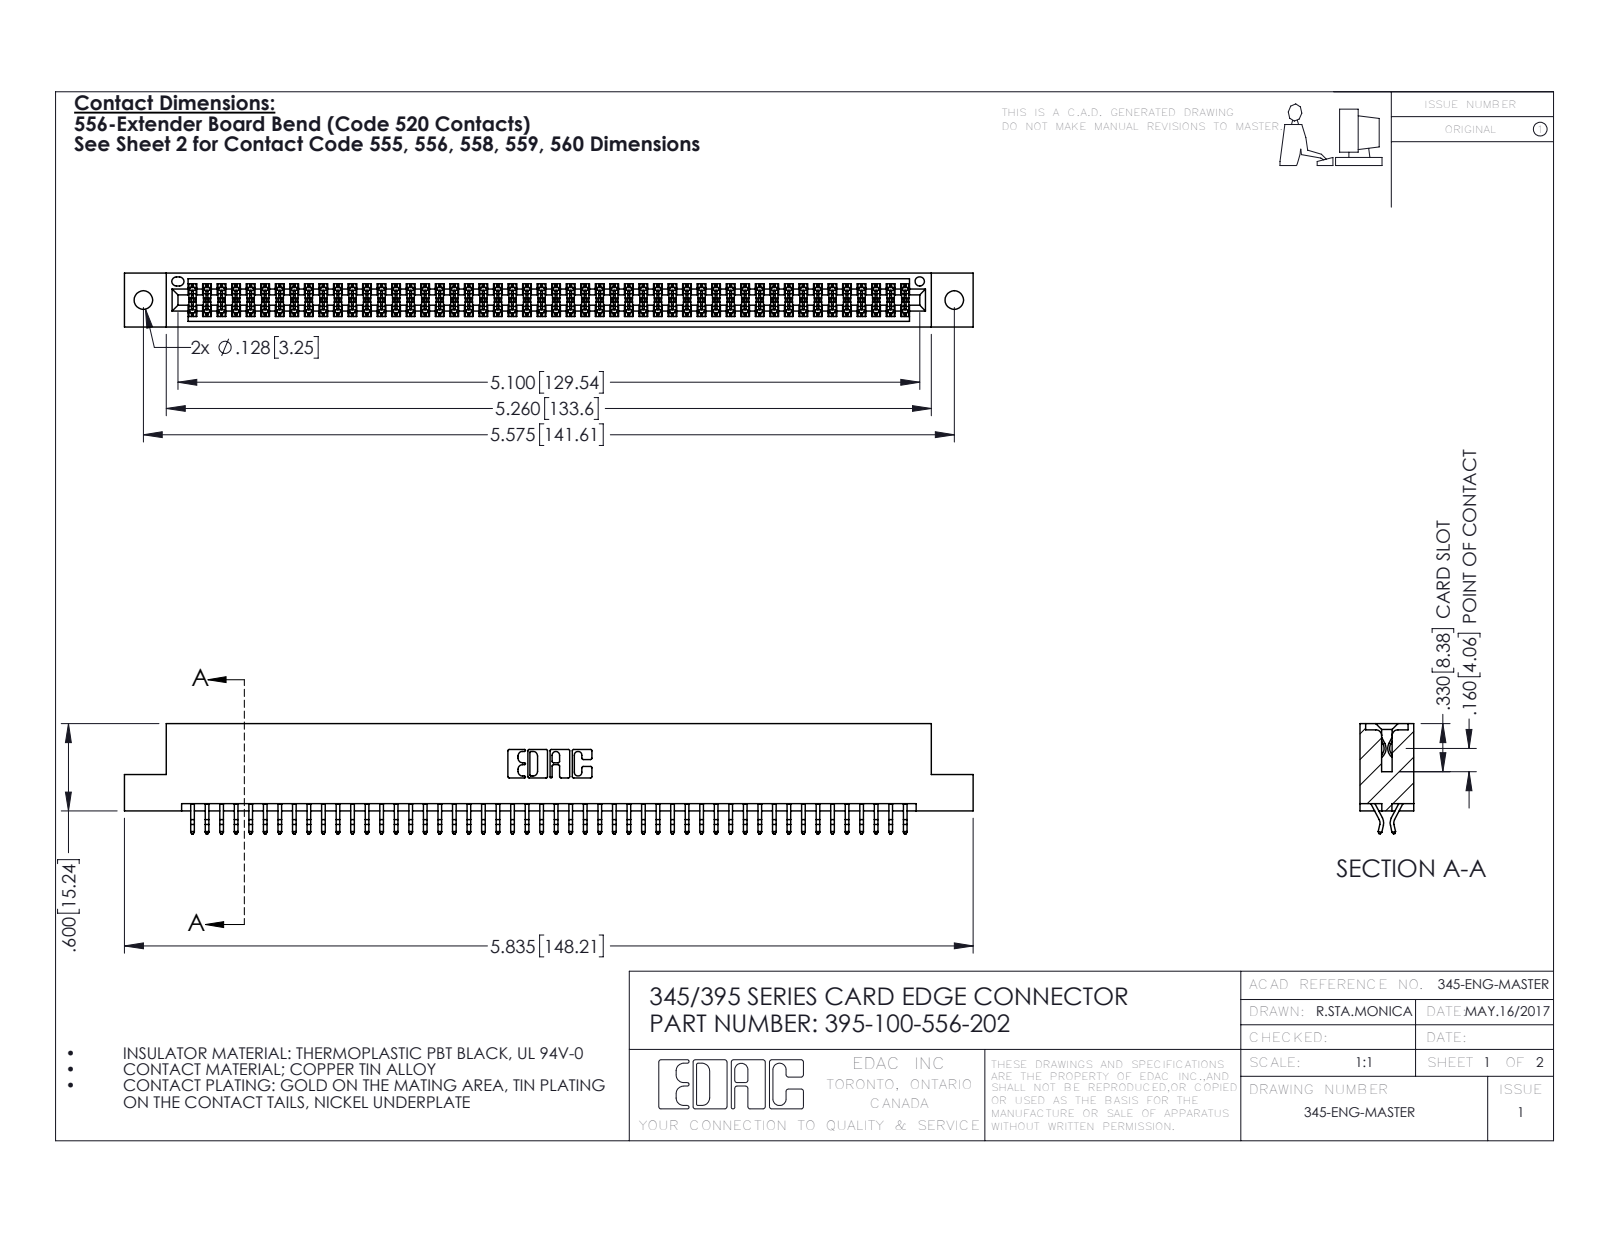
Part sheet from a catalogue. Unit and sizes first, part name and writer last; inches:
Units: inches
Overall size (bounding box): 5.835 × 0.757 × 0.37
Round holes (diameter × count): ⌀0.128 ×2, ⌀0.064 ×1
Partial cylindrical surfaces — rounded edges, fillets, slot ends (radius × count): R0.006 ×150, R0.01 ×22, R0.007 ×6, R0.031 ×6, R0.026 ×3, R0.01 ×2, R0.014 ×2, R0.019 ×2
Main face-to-face distances: 0.298, 0.072, 0.37, 0.2, 0.025, 0.098, 0.272, 0.225, 0.175, 0.149
Hole centre spacings: 0.27, 5.339, 5.575
Volume: 0.881 in³ · Surface area: 32.75 in²
Bodies: 101 solids, 5726 faces (3780 planar, 1946 cylindrical, 0 other)
Part name (STEP PRODUCT): 345-292-001_556 Tail; 345 Part_Flush Mounting Lugs - 0.128 Dia; 395-100-556-202
STEP written by: SolidWorks 2016 (CONFIG_CONTROL_DESIGN)
